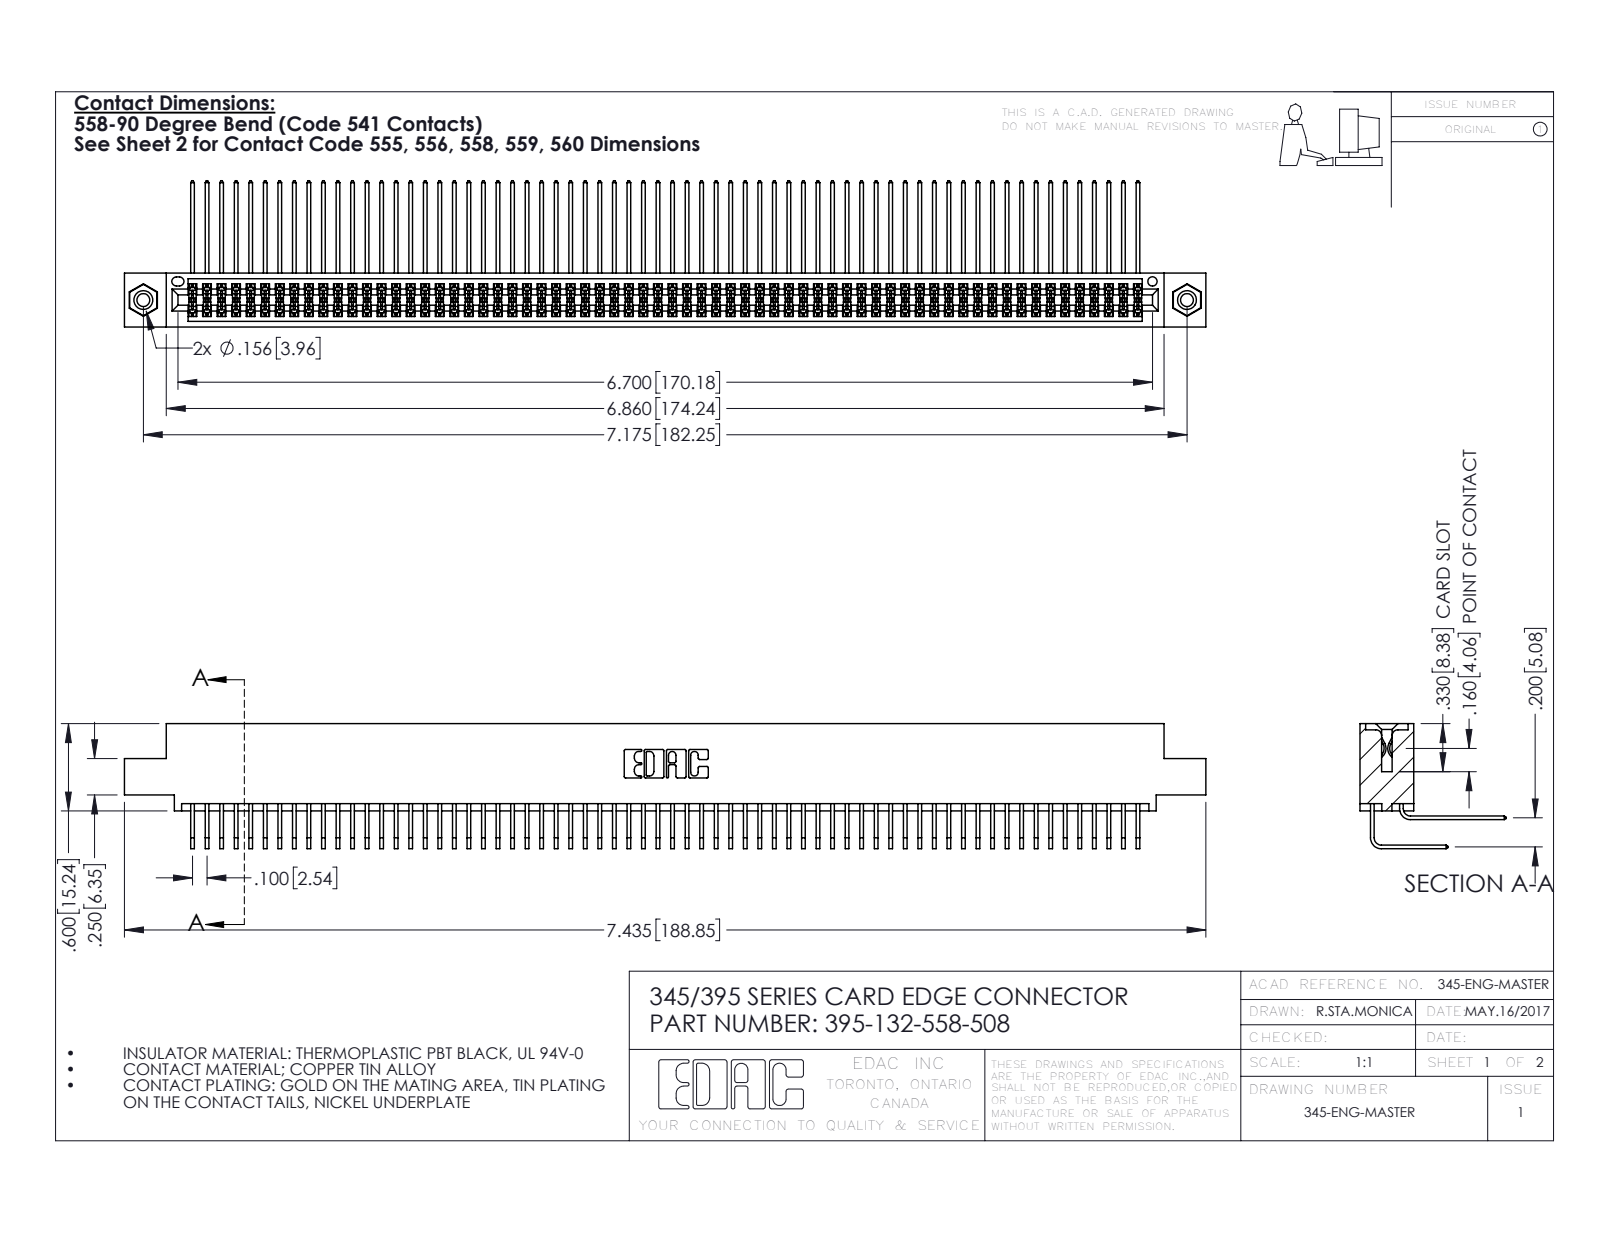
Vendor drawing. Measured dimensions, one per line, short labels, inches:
name: 395-132-558-508; 345-292-001_558 559 Tail - 1; 345 Part_0.110 Offset - 0.156 Dia-TI; 345-250-001_345-250-003-102 (+1 more)
written by: SolidWorks 2016 (CONFIG_CONTROL_DESIGN)
unit: in
bodies: 135 solids, 7054 faces (4736 planar, 2302 cylindrical, 16 other)
size: 7.435 × 1.005 × 0.859
volume: 1.175 in³; area: 50.54 in²
holes: 2× ⌀0.089, 2× ⌀0.125, 2× ⌀0.156, 1× ⌀0.064
bosses: 2× ⌀0.155
rounds: 199× R0.006, 22× R0.01, 6× R0.007, 6× R0.031, 3× R0.026, 2× R0.014, 2× R0.019, 2× R0.022
face distances: 0.072, 0.298, 0.2, 0.37, 0.098, 0.272, 0.025, 0.225, 0.025, 0.175
hole spacings: 0.27, 6.939, 7.175
